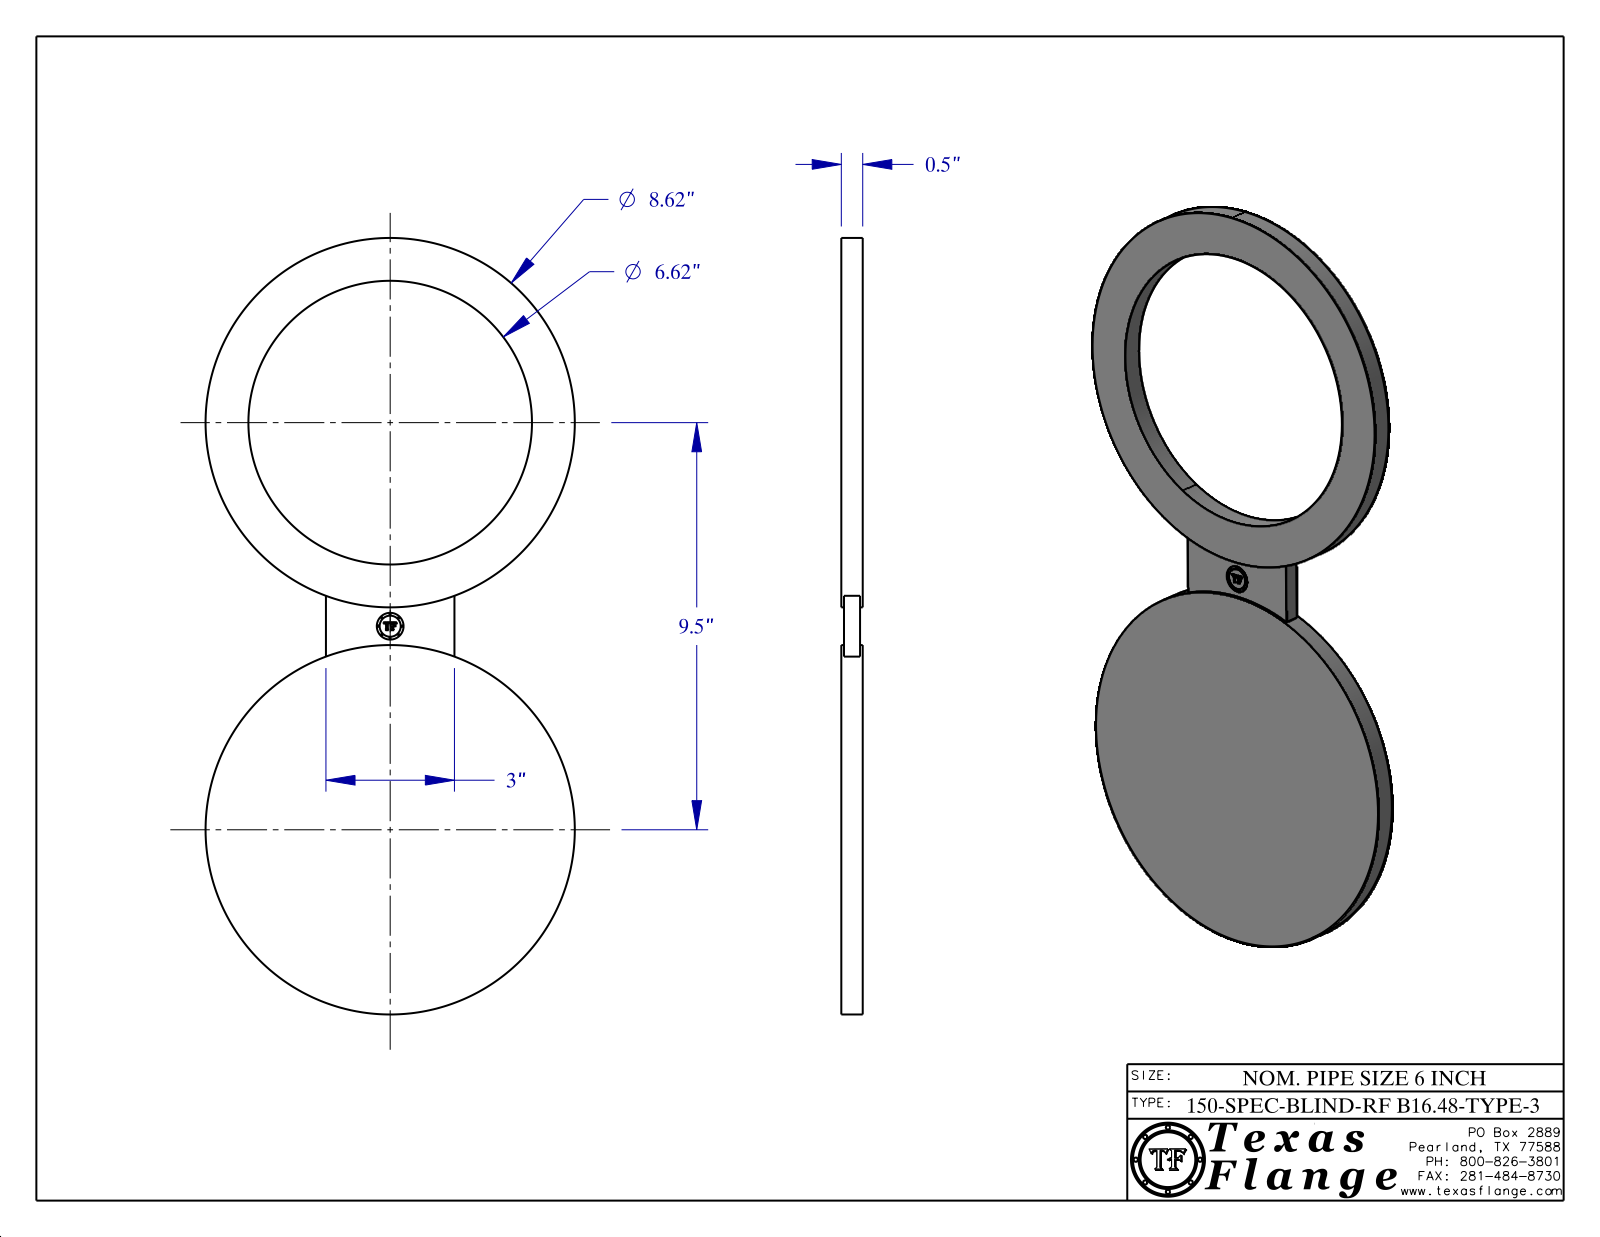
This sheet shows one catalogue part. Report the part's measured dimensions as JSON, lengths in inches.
{"part_name": "6-150-SPEC-BLIND-RF-B16.48-TYPE-3", "step_written_by": "CATIA V5 STEP AP214 (AUTOMOTIVE_DESIGN)", "units": "inches", "bodies": {"solids": 1, "faces": 399, "planar": 373, "cylindrical": 26, "other": 0}, "overall_size": [18.12, 8.62, 0.5], "volume_in3": 42.34, "surface_area_in2": 207.3, "round_holes": [[0.625, 1], [6.62, 1]], "round_bosses_or_shafts": [[0.038, 8], [8.62, 2], [0.492, 1]], "face_to_face_distances": [0.5, 0.063, 0.437, 0.375, 3, 0.422, 0.36, 0.015, 0.078, 1.437], "hole_center_spacings": [4.75]}
